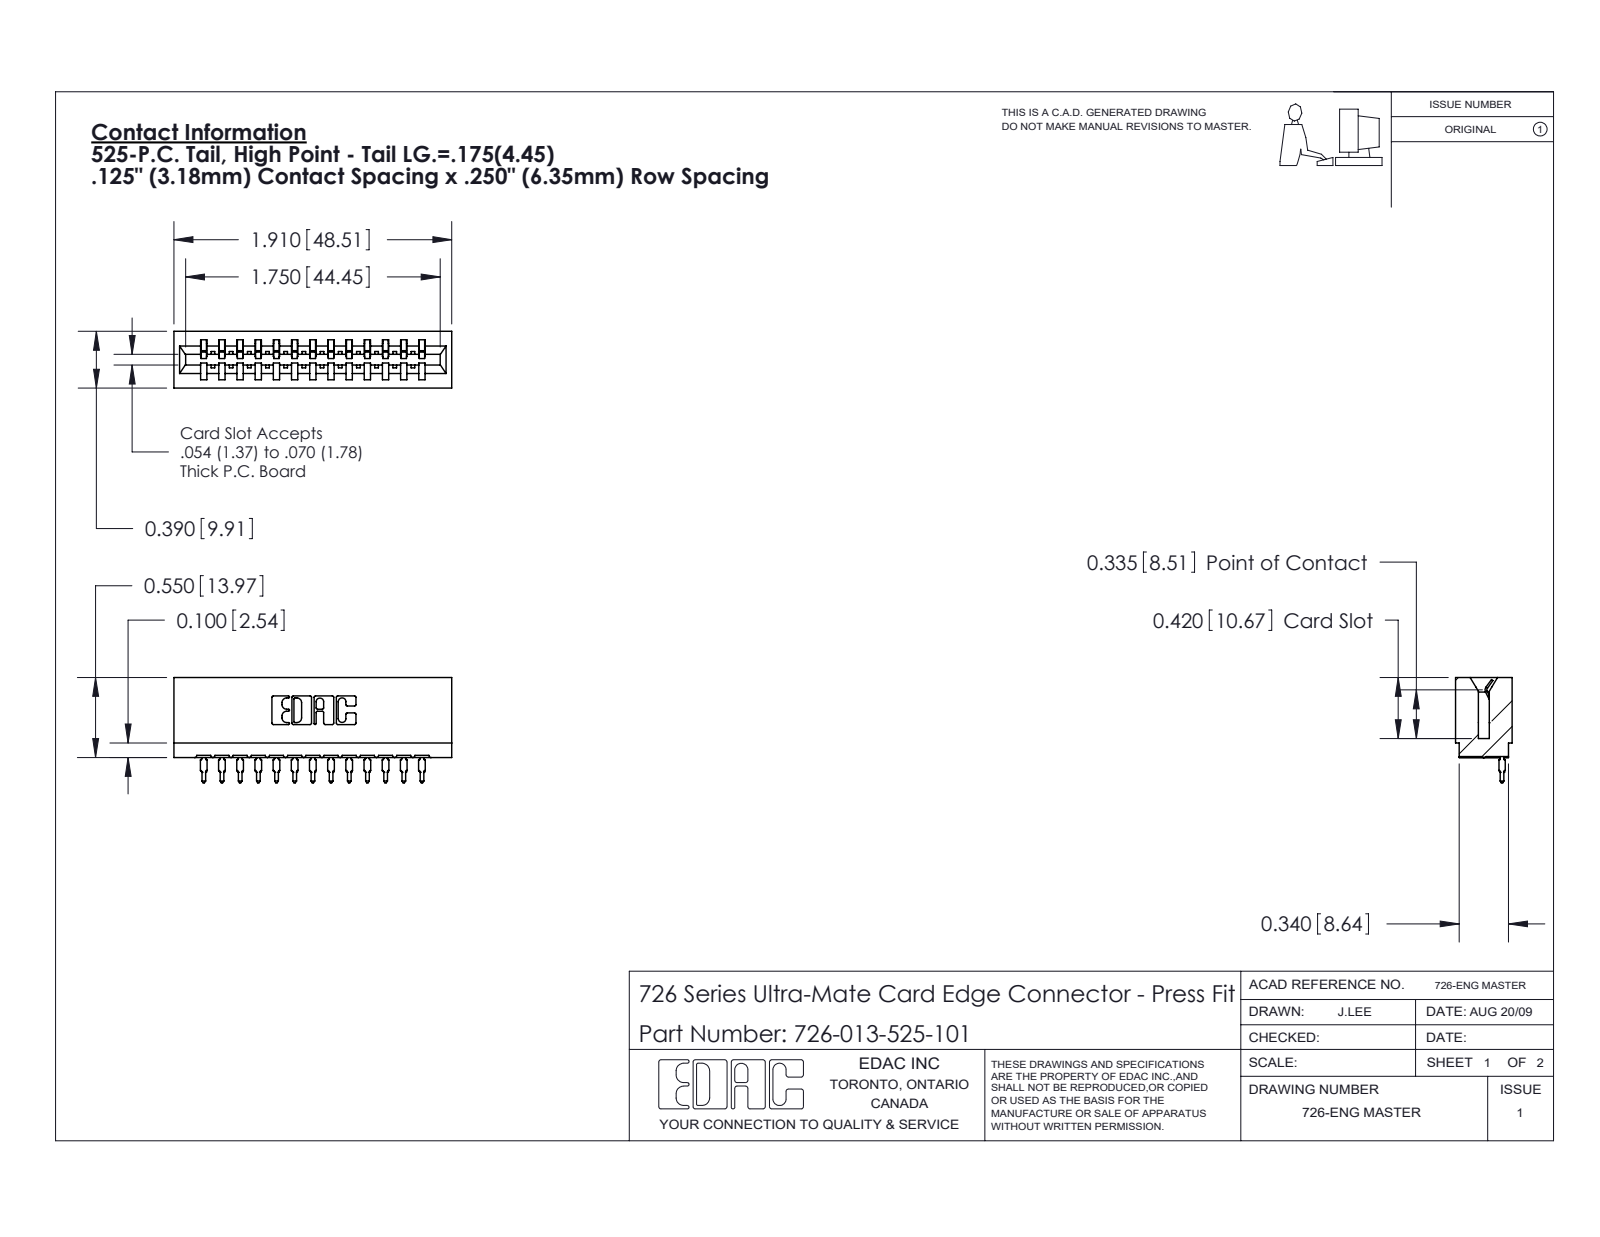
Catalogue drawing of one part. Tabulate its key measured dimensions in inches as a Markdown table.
| quantity | value |
| --- | --- |
| part name | 726 Part_.515 Slot Depth - 01; 726-013-525-101; 746-292-001_525 |
| STEP written by | SolidWorks 2020 (CONFIG_CONTROL_DESIGN) |
| units | inches |
| bodies | 14 solids, 1501 faces (874 planar, 289 cylindrical, 338 other) |
| overall size | 1.91 × 0.724 × 0.39 |
| volume | 0.274 in³ |
| surface area | 9.845 in² |
| partial cylindrical surfaces (radius × count) | 0.021 × 26, 0.01 × 22, 0.015 × 14, 0.007 × 6, 0.031 × 6, 0.005 × 4, 0.011 × 4, 0.026 × 3 |
| main face-to-face distances | 0.25, 0.057, 0.333, 0.5, 0.75, 0.39, 0.125, 0.542, 0.125, 0.625 |
